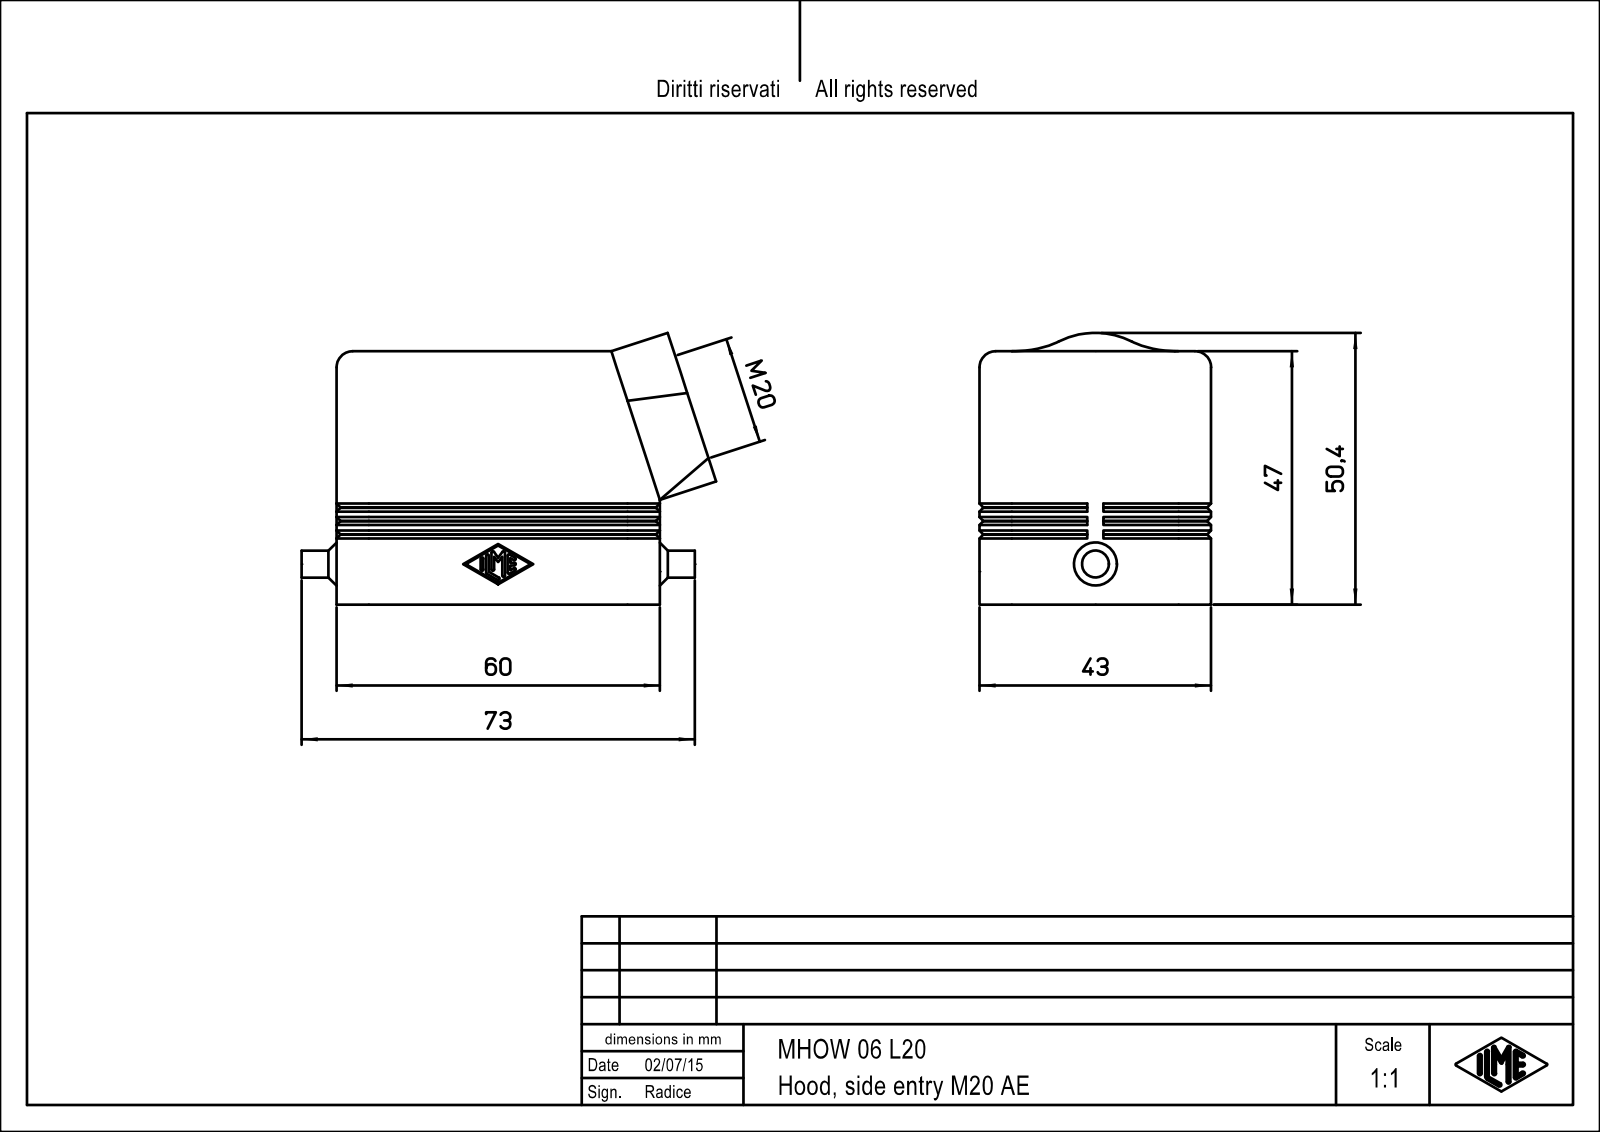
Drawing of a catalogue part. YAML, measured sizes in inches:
part_name: "MHOW_06_L20"
step_written_by: "Creo Elements/Direct Modeling 18.1F 24-Jul-2014 (C) Parametric Technology GmbH (AUTOMOTIVE_DESIGN)"
units: inches
bodies: {solids: 1, faces: 269, planar: 140, cylindrical: 77, other: 52}
overall_size: [3.03, 1.985, 1.693]
volume: 2.772
surface_area: 36.2
round_holes:
  - {diameter: 0.097, count: 4}
  - {diameter: 0.157, count: 4}
  - {diameter: 0.554, count: 1}
  - {diameter: 0.75, count: 1}
round_bosses_or_shafts:
  - {diameter: 0.197, count: 1}
partial_cylinders:
  - {radius: 0.01, count: 14}
  - {radius: 0.118, count: 7}
  - {radius: 0.079, count: 4}
  - {radius: 0.209, count: 4}
  - {radius: 0.236, count: 4}
face_to_face_distances: [0.118, 1.575, 1.457, 1.693, 0.453, 0.335, 1.909, 1.791, 2.244, 1.24]
hole_center_spacings: [1.063, 1.732, 2.032]
